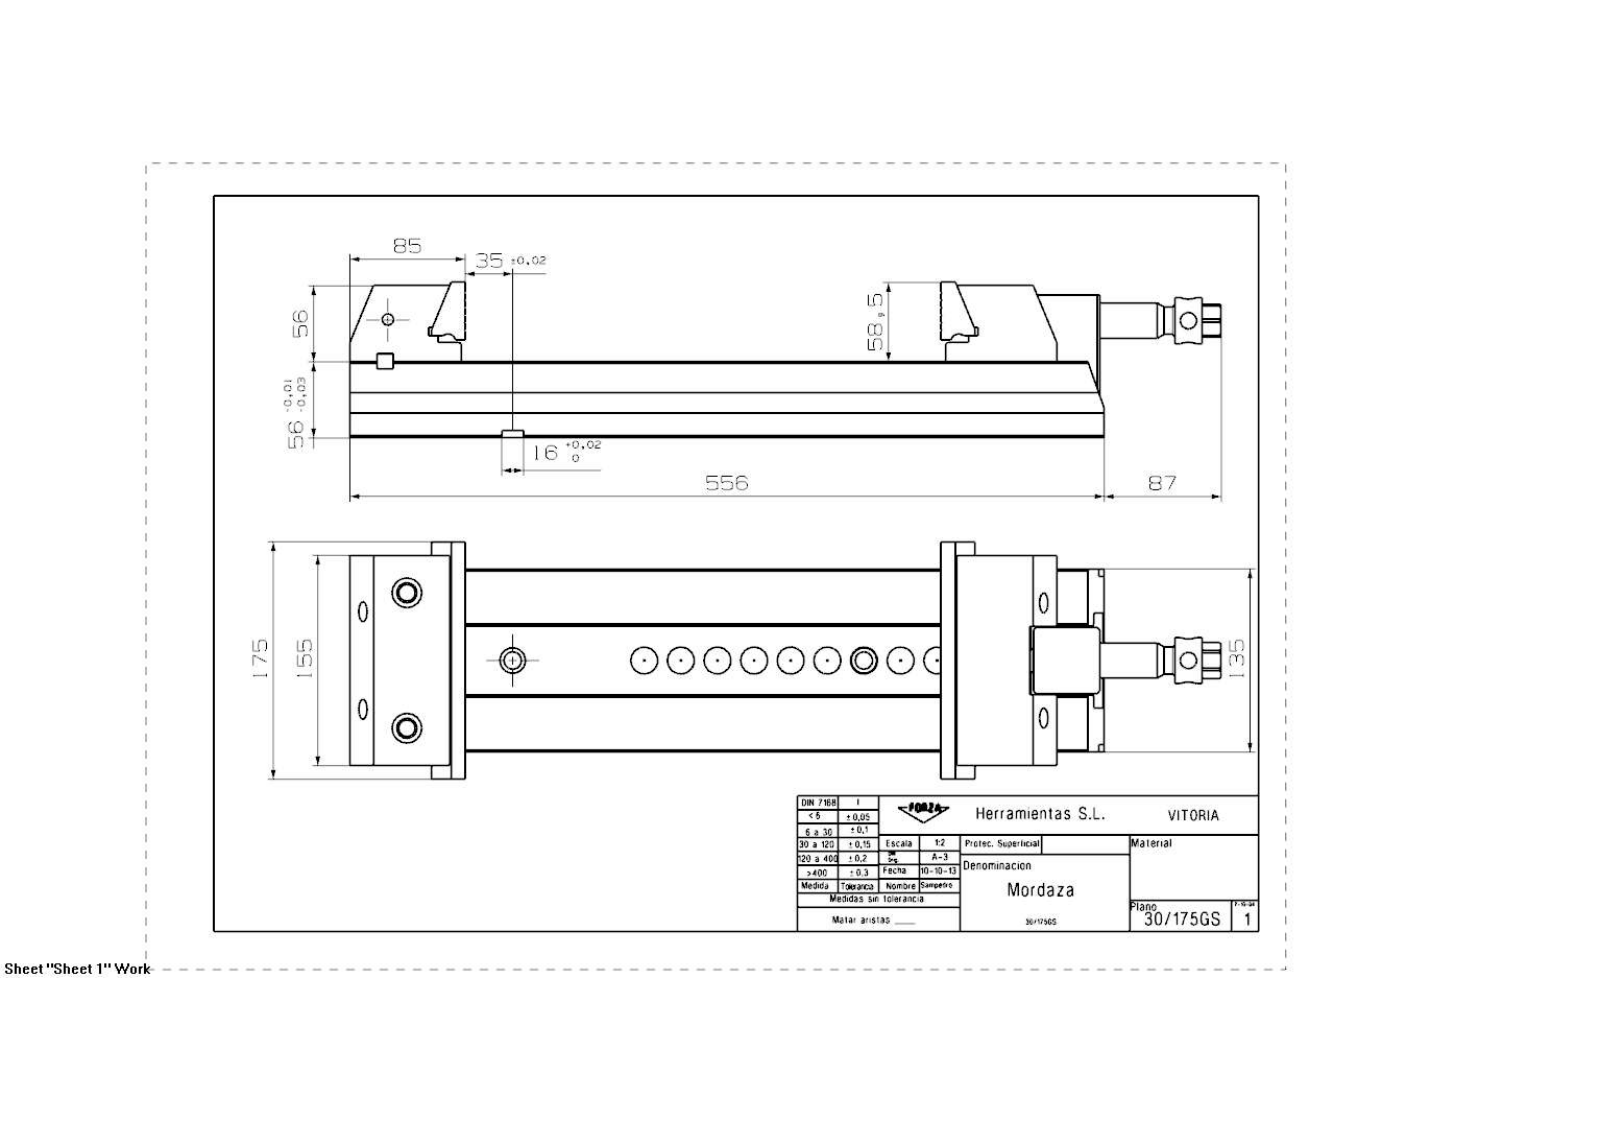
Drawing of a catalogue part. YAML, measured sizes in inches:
part_name: "30_175GS_Mordaza"
step_written_by: "SIEMENS PLM Software NX 7.5 (CONFIG_CONTROL_DESIGN)"
units: inches
bodies: {solids: 12, faces: 475, planar: 312, cylindrical: 95, other: 68}
overall_size: [25.285, 6.89, 4.508]
volume: 272.8
surface_area: 854.8
round_holes:
  - {diameter: 0.512, count: 6}
  - {diameter: 0.591, count: 6}
  - {diameter: 0.748, count: 6}
  - {diameter: 0.204, count: 5}
  - {diameter: 0.275, count: 4}
  - {diameter: 0.335, count: 4}
  - {diameter: 0.417, count: 4}
  - {diameter: 0.346, count: 3}
  - {diameter: 0.374, count: 2}
  - {diameter: 0.394, count: 2}
  - {diameter: 0.472, count: 2}
  - {diameter: 0.487, count: 2}
round_bosses_or_shafts:
  - {diameter: 1.339, count: 1}
  - {diameter: 1.331, count: 1}
  - {diameter: 1.024, count: 1}
  - {diameter: 0.787, count: 1}
  - {diameter: 0.65, count: 1}
partial_cylinders:
  - {radius: 0.315, count: 4}
  - {radius: 0.787, count: 4}
  - {radius: 0.063, count: 2}
  - {radius: 0.236, count: 2}
  - {radius: 0.276, count: 2}
  - {radius: 0.157, count: 1}
  - {radius: 0.354, count: 1}
  - {radius: 0.413, count: 1}
face_to_face_distances: [2.205, 0.953, 1.252, 1.28, 1.673, 4.035, 5.315, 2.165, 0.217, 0.039]
hole_center_spacings: [0.256, 3.091, 2.835, 3.346, 4.176, 1.093, 1.094, 1.181]
